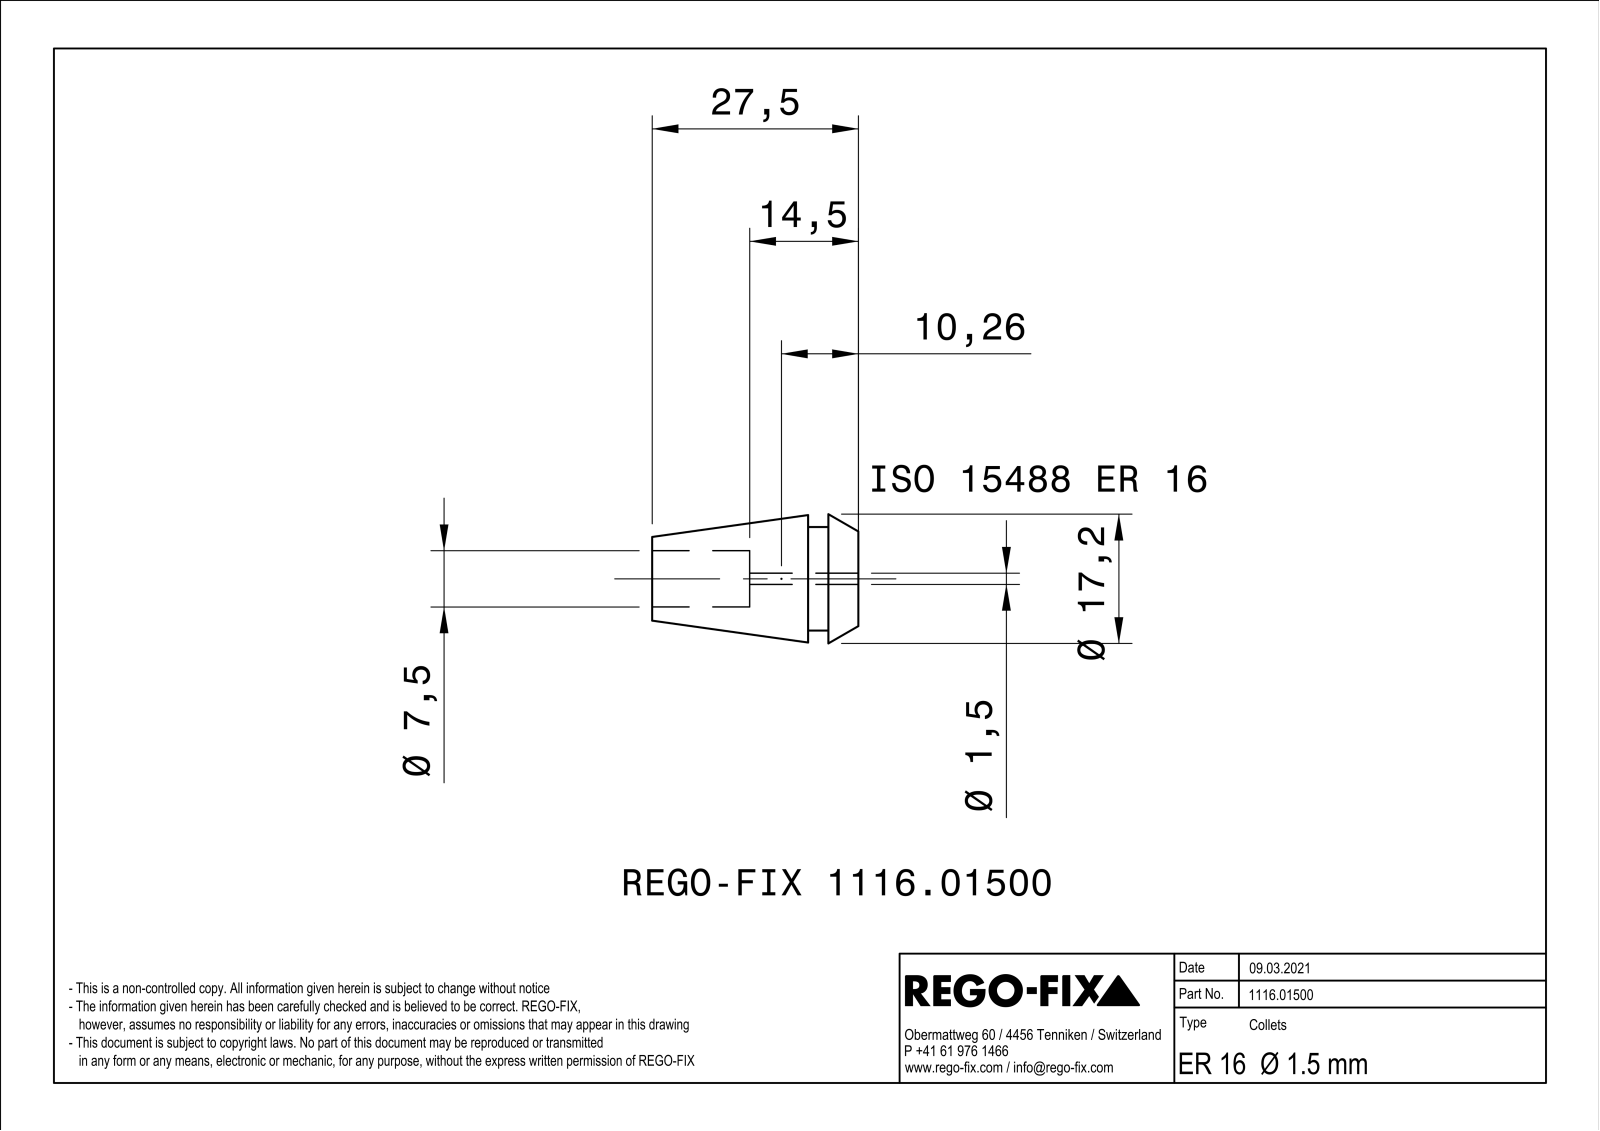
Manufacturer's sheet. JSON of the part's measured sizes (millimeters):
{"part_name": "NOCUT", "step_written_by": "SIEMENS PLM Software Solid Edge ST10 (AUTOMOTIVE_DESIGN)", "units": "millimeters", "bodies": {"solids": 1, "faces": 224, "planar": 108, "cylindrical": 28, "other": 88}, "overall_size": [27.5, 17.24, 17.24], "volume_mm3": 3041, "surface_area_mm2": 5081, "round_holes": [[7.5, 1]], "round_bosses_or_shafts": [[13.8, 1]], "partial_cylinders_radius": [[0.75, 1]], "face_to_face_distances": [0.46, 0.44, 0.45, 4, 6.7, 2.7, 3.27, 3.28, 3.72, 3.73]}
